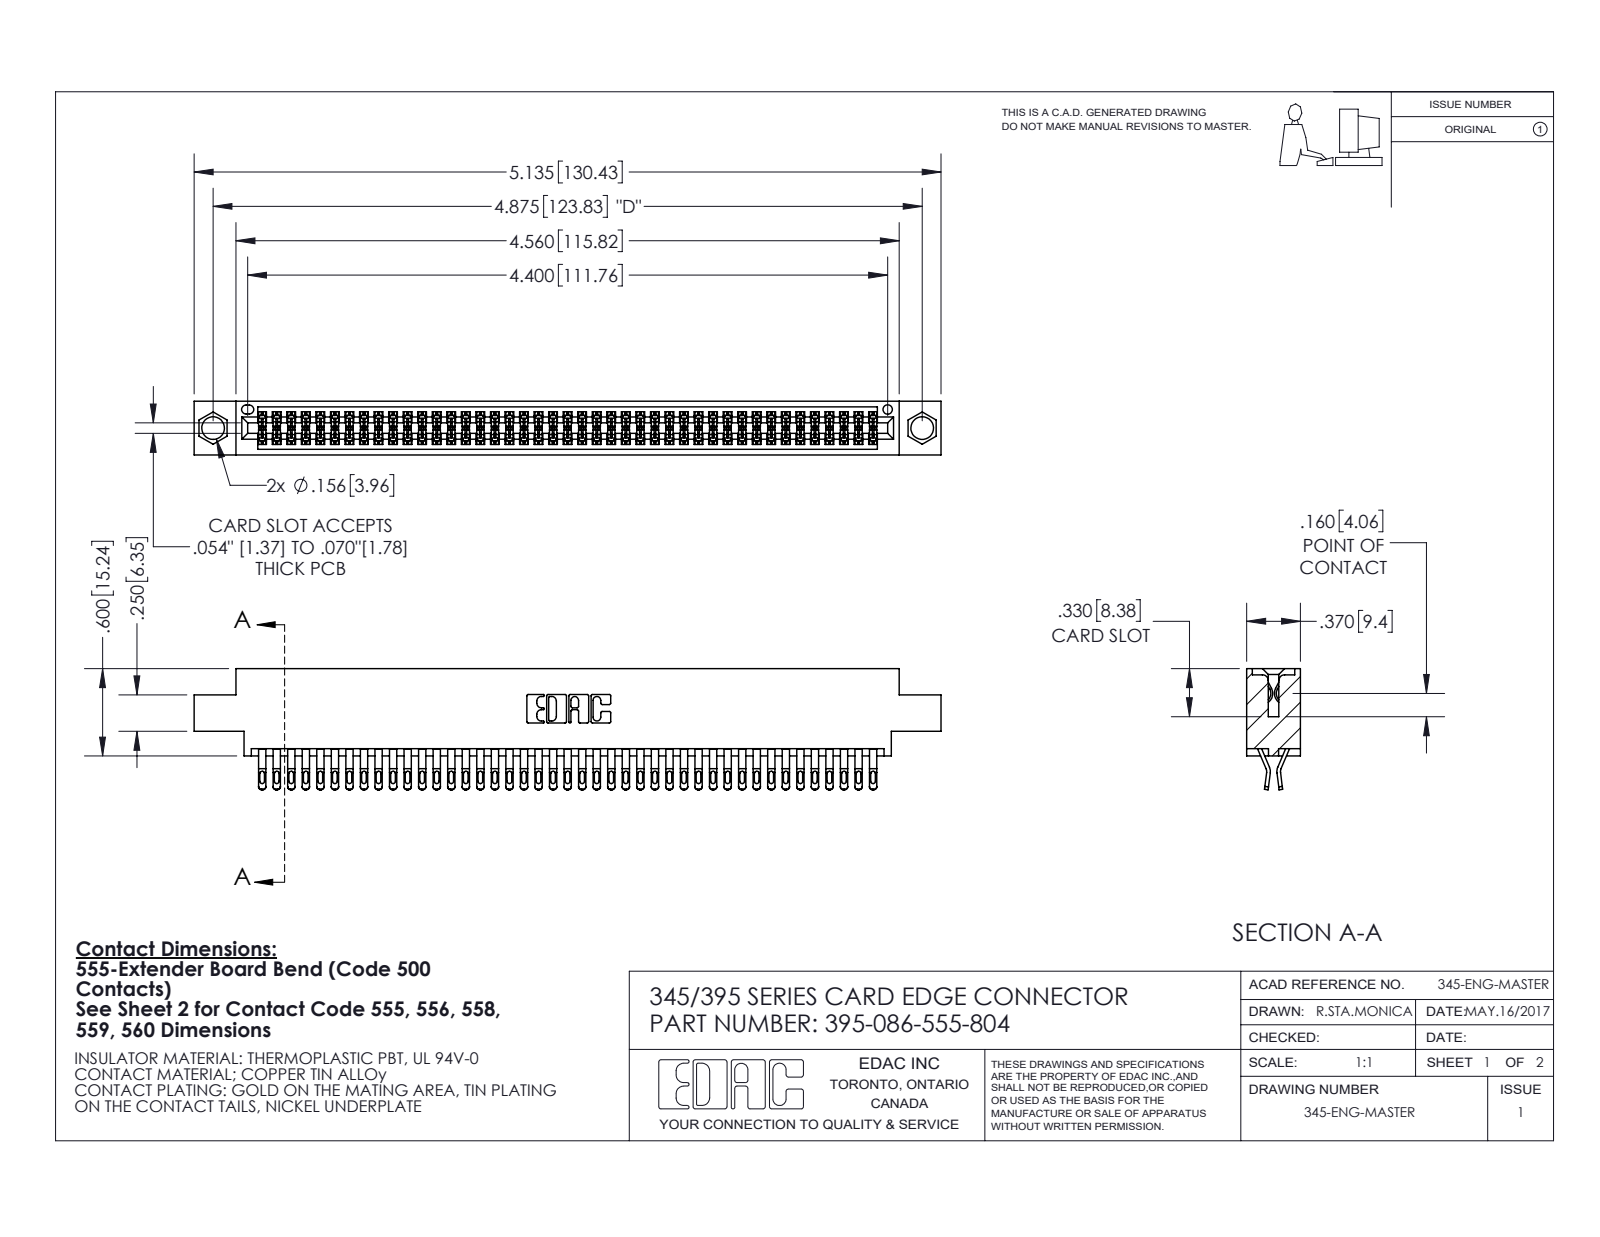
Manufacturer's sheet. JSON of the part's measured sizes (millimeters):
{"part_name": "395-086-555-804; 345 Part_0.170 Offset - 0.156 Dia-TI; 345-292-001_555 Tail", "step_written_by": "SolidWorks 2020 (CONFIG_CONTROL_DESIGN)", "units": "millimeters", "bodies": {"solids": 87, "faces": 4960, "planar": 2764, "cylindrical": 2196, "other": 0}, "overall_size": [130.4, 21.1, 9.4], "volume_mm3": 12700, "surface_area_mm2": 19670, "round_holes": [[4, 2], [1.6, 1]], "partial_cylinders_radius": [[0.4, 215], [0.2, 172], [0.5, 172], [0.3, 22], [0.2, 6], [0.8, 6], [0.7, 3], [0.3, 2]], "face_to_face_distances": [1.8, 7.6, 9.4, 0.6, 5.1, 2.5, 6.9, 5.7, 4.4, 3.8], "hole_center_spacings": [6.9, 117.8, 123.8]}
